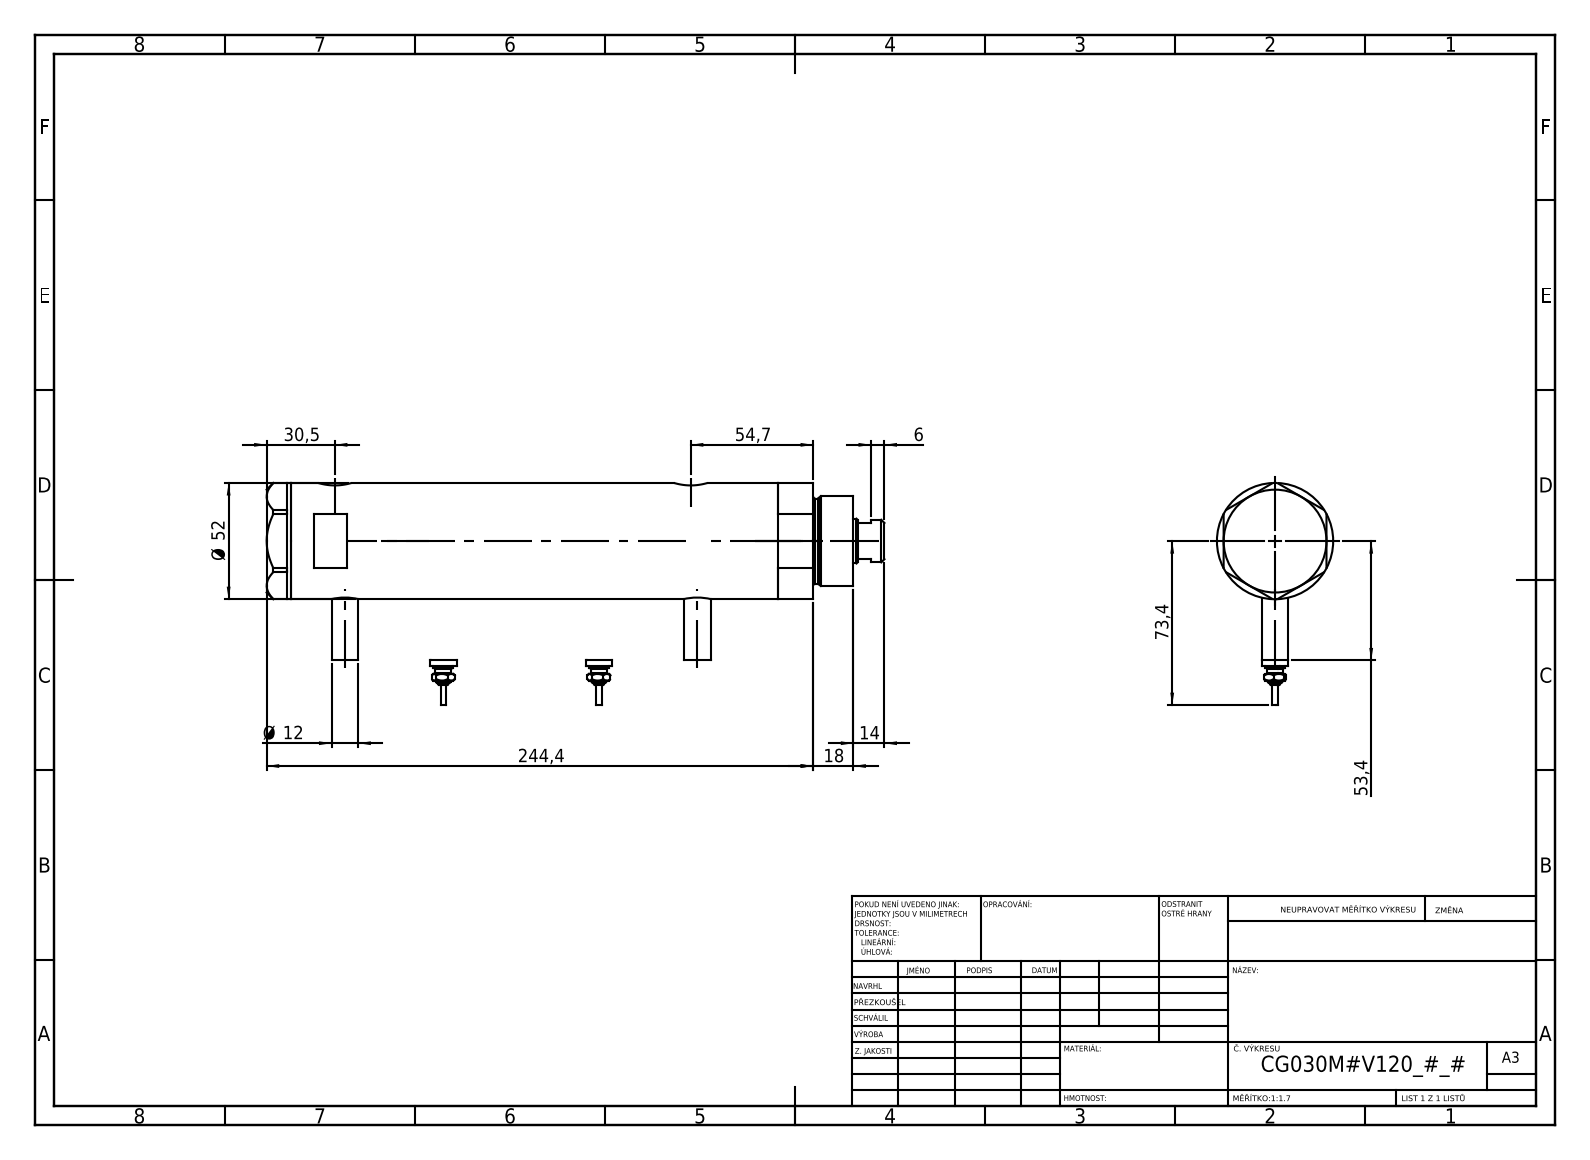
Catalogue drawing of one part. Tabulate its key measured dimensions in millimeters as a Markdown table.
| quantity | value |
| --- | --- |
| part name | V270CG_BACK; V270CG_MIDDLE; V270CG_FRONT; Switch (+1 more) |
| STEP written by | SolidWorks 2019 (CONFIG_CONTROL_DESIGN) |
| units | millimeters |
| bodies | 6 solids, 226 faces (93 planar, 69 cylindrical, 64 other) |
| overall size | 276.3 × 99.4 × 52 |
| volume | 498 069 mm³ |
| surface area | 108 932 mm² |
| round holes (diameter × count) | 9.73 × 2, 12.5 × 2, 15 × 2, 6.5 × 1, 20 × 1, 21.5 × 1, 30 × 1, 33 × 1, 44 × 1 |
| round bosses / shafts (diameter × count) | 12 × 4, 9 × 2, 7 × 2, 4.5 × 2, 2.5 × 2, 52 × 1, 40 × 1, 38 × 1 |
| main face-to-face distances | 181.5, 23.8, 157.7, 11, 34.8, 192.5, 46, 36.4, 228.9, 217.9 |
| hole center spacings | 2.9, 4.5, 154.7, 157.6, 159.2, 162.1 |
